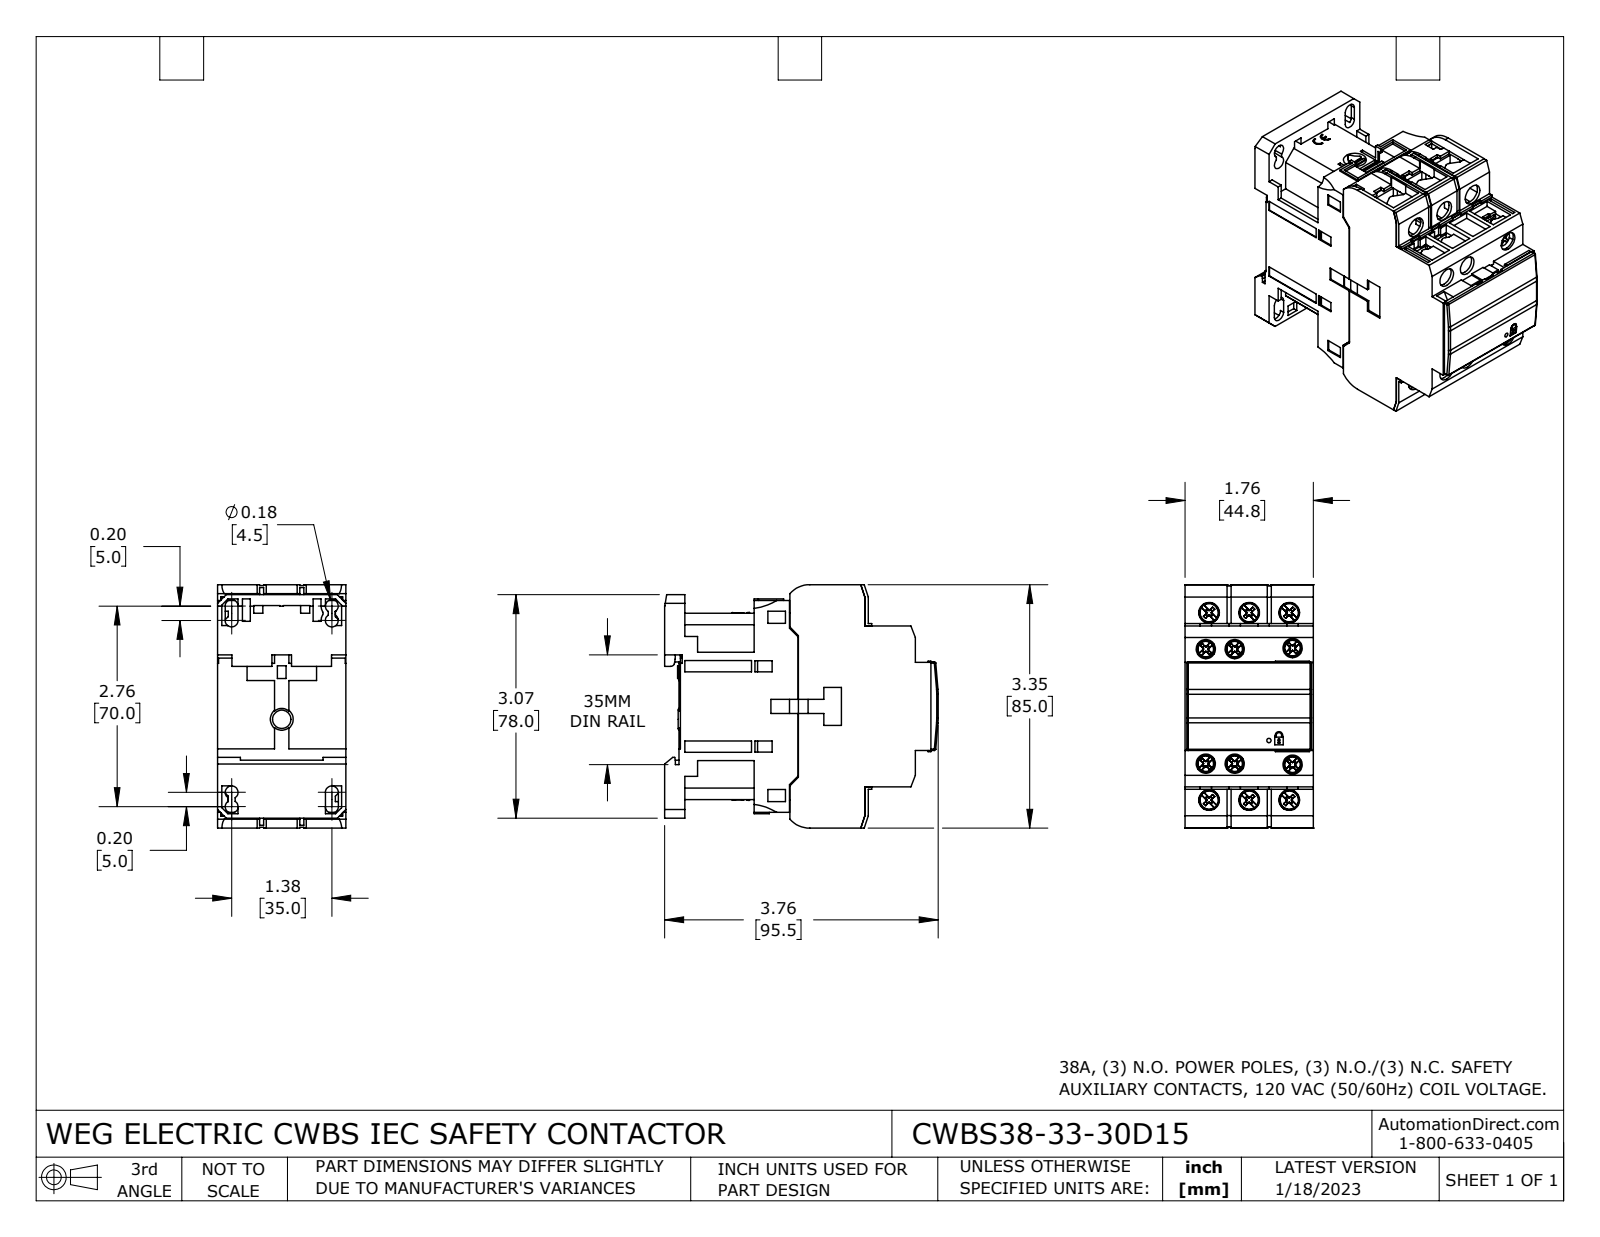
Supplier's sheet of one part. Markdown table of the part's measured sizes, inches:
| quantity | value |
| --- | --- |
| part name | CWBS38-33-30D15 |
| STEP written by | SolidWorks 2021 (CONFIG_CONTROL_DESIGN) |
| units | inches |
| bodies | 42 solids, 2461 faces (1808 planar, 446 cylindrical, 207 other) |
| overall size | 3.76 × 3.346 × 1.764 |
| volume | 14.49 in³ |
| surface area | 108.8 in² |
| round holes (diameter × count) | 0.124 × 6, 0.142 × 6, 0.264 × 6, 0.283 × 6, 0.177 × 4, 0.059 × 1 |
| round bosses / shafts (diameter × count) | 0.201 × 6, 0.169 × 6, 0.157 × 6, 0.138 × 6, 0.107 × 4, 0.107 × 2 |
| partial cylindrical surfaces (radius × count) | 0.02 × 42, 0.028 × 24, 0.071 × 12, 0.081 × 12, 0.964 × 12, 1.079 × 12, 2.128 × 12, 3.127 × 12 |
| main face-to-face distances | 1.764, 0.047, 1.691, 0.132, 1.823, 0.024, 0.217, 3.445, 0.276, 1.717 |
| hole center spacings | 0.551, 2.633, 2.575, 0.165, 0.174, 0.197, 0.398, 0.488 |
